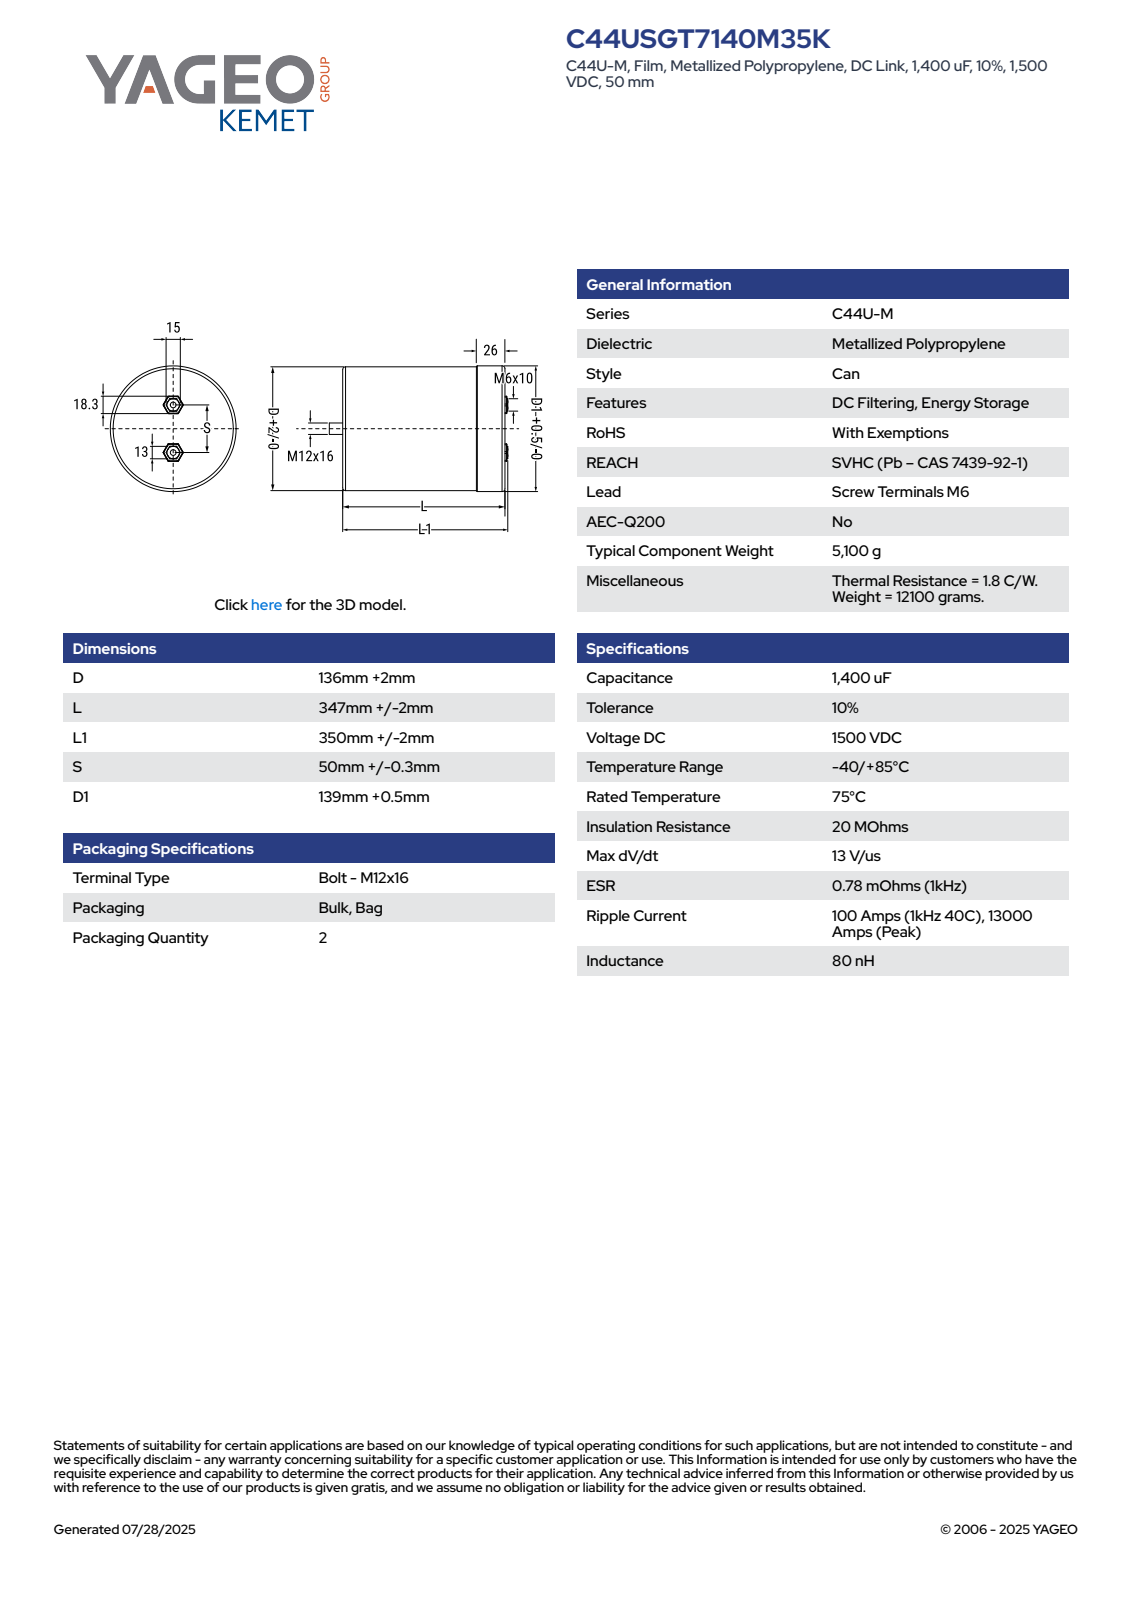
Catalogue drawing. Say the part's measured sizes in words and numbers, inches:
The part is named "CFP_C44UMH_136X347_D138L349S50L1352D1139.5". Its 3-D file was written by "SolidWorks 2014 (AUTOMOTIVE_DESIGN)". It is 1 solid with 92 faces: 44 planar, 17 cylindrical and 31 other. Overall it measures 14.488 by 5.492 by 5.492 inches. Its volume is 319.2 cubic inches and its surface area 284.1 square inches. Round holes: 2 of diameter 0.236. Round bosses or shafts: 2 of diameter 0.512, 1 of diameter 5.492, 1 of diameter 5.433, 1 of diameter 0.472. Partial cylindrical surfaces (rounded edges, fillets, slot ends): 1 of radius 2.717. The main face-to-face distances are 13.74, 12.717, 1.024, 13.819, 1.102, 0.079, 13.858, 1.142, 0.118, 0.039. The hole center spacings are 1.969.
